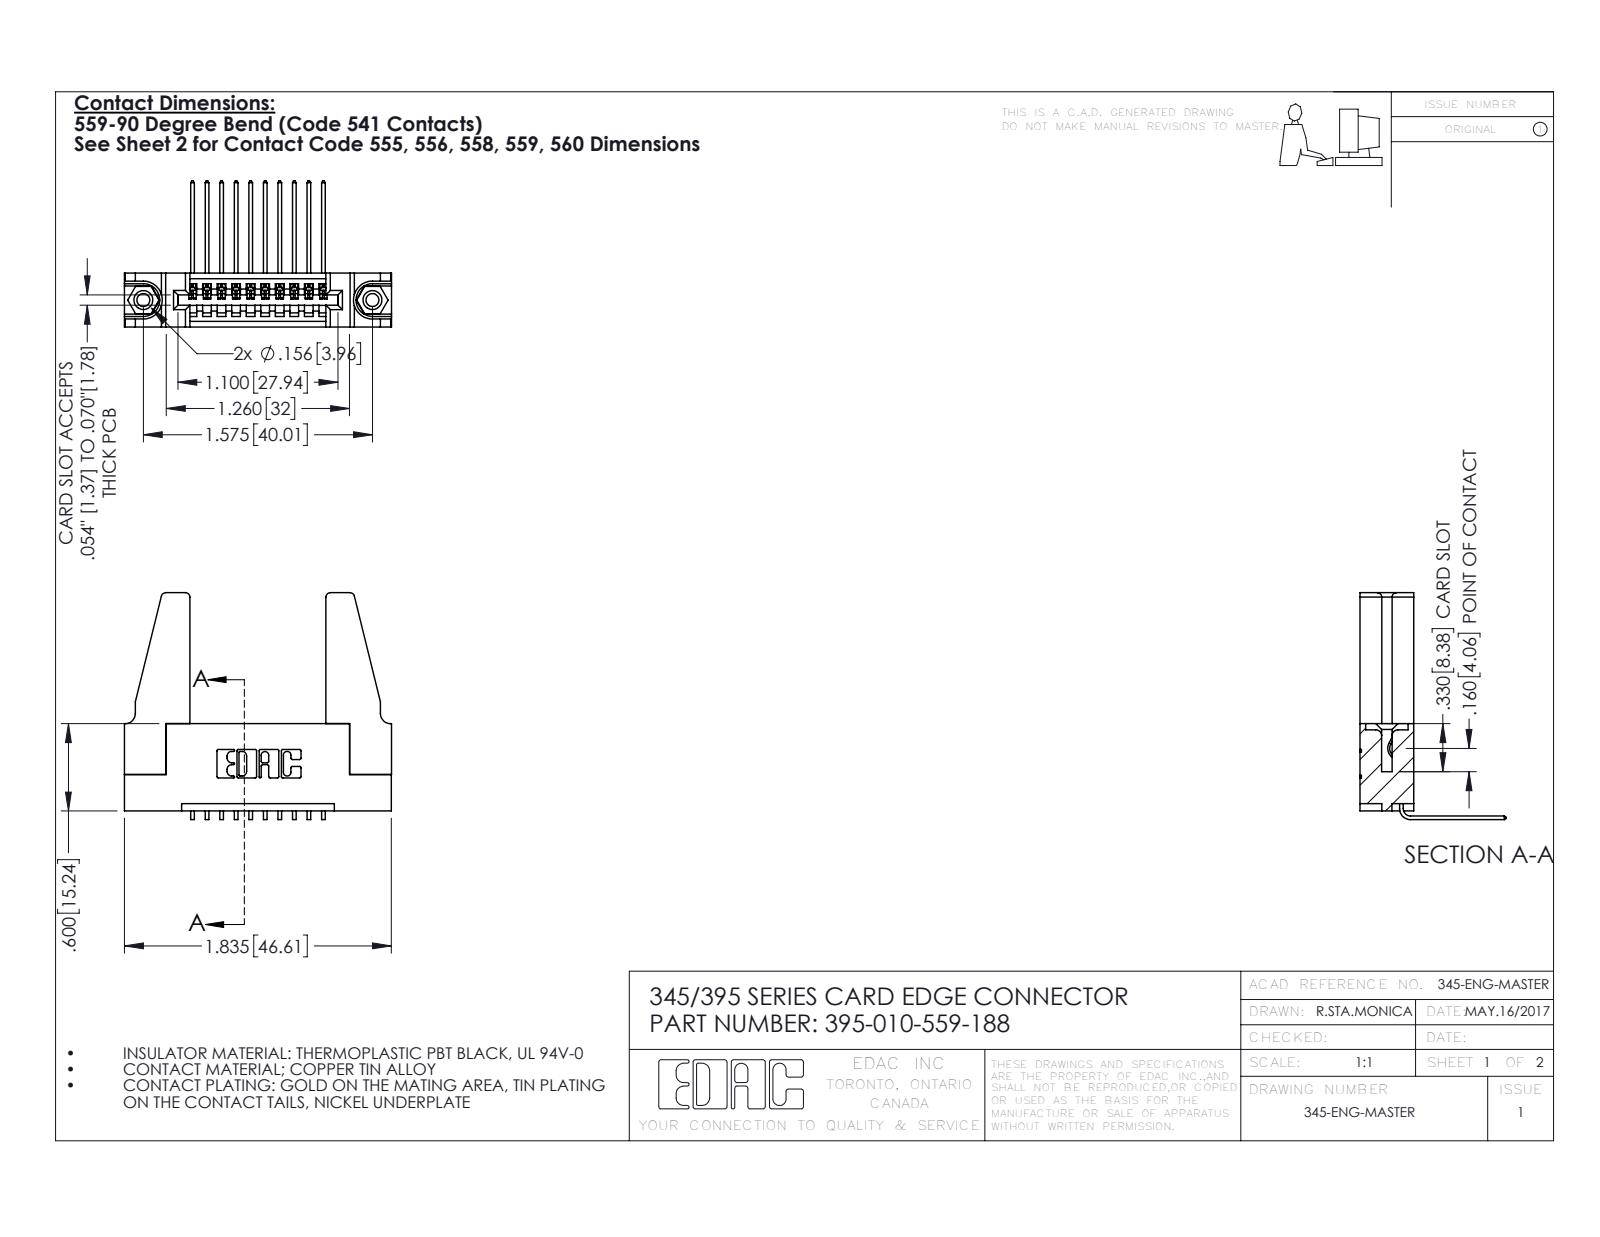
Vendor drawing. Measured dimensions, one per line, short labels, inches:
name: 345-250-001_345-250-001-102; 395-010-559-188; 345-292-001_558 559 Tail - 1; 345 Part_Flush Mounting Lugs - 0.156 Dia-TH (+1 more)
written by: SolidWorks 2016 (CONFIG_CONTROL_DESIGN)
unit: in
bodies: 15 solids, 850 faces (572 planar, 262 cylindrical, 16 other)
size: 1.836 × 1.559 × 1.005
volume: 0.455 in³; area: 13.13 in²
holes: 2× ⌀0.089, 2× ⌀0.125, 2× ⌀0.156, 1× ⌀0.064
bosses: 2× ⌀0.155
rounds: 22× R0.01, 20× R0.006, 8× R0.03, 6× R0.007, 6× R0.031, 3× R0.026, 2× R0.031, 2× R0.04
face distances: 0.37, 0.072, 0.298, 0.2, 0.098, 0.272, 0.025, 0.148, 0.15, 0.25
hole spacings: 0.27, 1.344, 1.575
